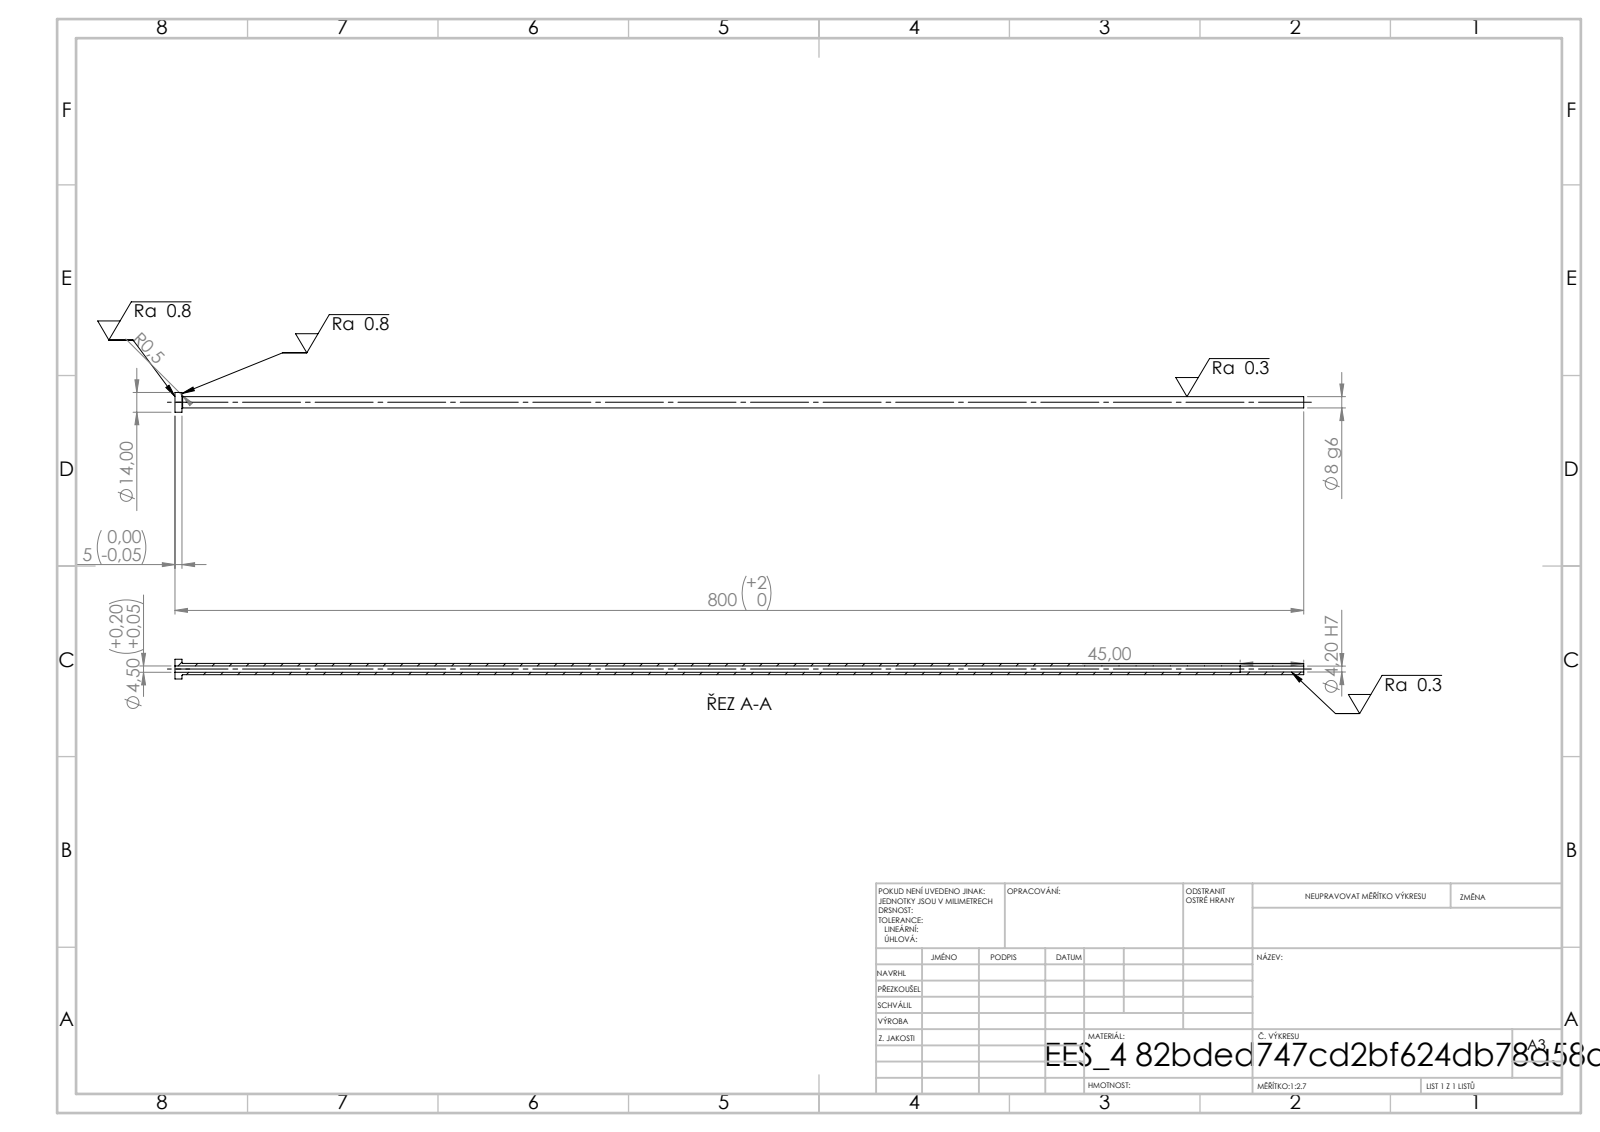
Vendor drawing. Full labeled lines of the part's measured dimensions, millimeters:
STEP written by: SolidWorks 2019 (CONFIG_CONTROL_DESIGN)
Units: millimetres
Bodies: 1 solid, 14 faces (4 planar, 8 cylindrical, 2 other)
Overall size (bounding box): 800 × 14 × 14
Volume: 28 101 mm³ · Surface area: 31 743 mm²
Round holes (diameter × count): ⌀4.2 ×1, ⌀4.5 ×1
Round bosses / shafts (diameter × count): ⌀14 ×1, ⌀8 ×1
Main face-to-face distances: 5, 800, 795, 755, 750, 45
